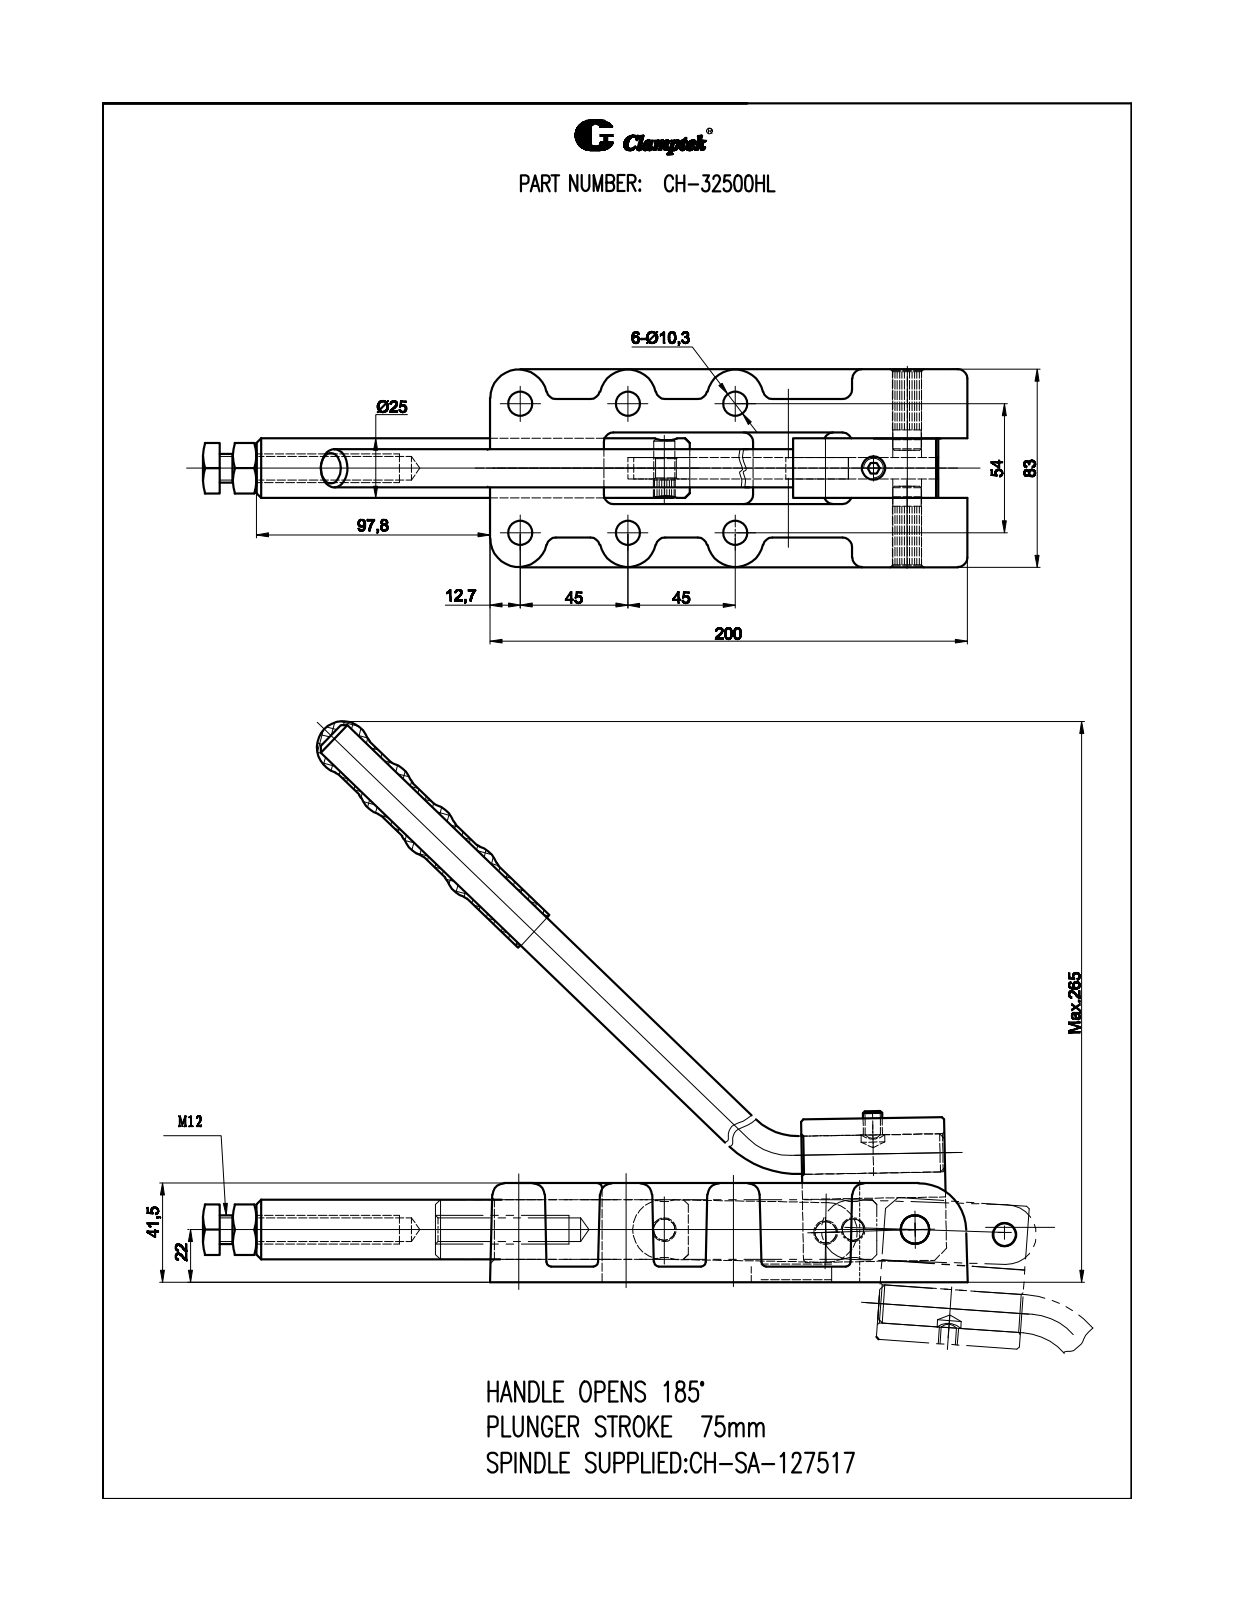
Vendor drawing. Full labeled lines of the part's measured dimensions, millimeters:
Part name (STEP PRODUCT): CH-32500HL
STEP written by: SolidWorks 2008 (CONFIG_CONTROL_DESIGN)
Units: millimetres
Bodies: 13 solids, 1027 faces (273 planar, 336 cylindrical, 418 other)
Overall size (bounding box): 318 × 281.65 × 78
Volume: 586 040 mm³ · Surface area: 159 482 mm²
Round holes (diameter × count): ⌀10.3 ×6, ⌀9.02 ×2, ⌀9.2 ×2, ⌀4 ×1, ⌀6.8 ×1, ⌀9 ×1, ⌀9.05 ×1, ⌀10 ×1, ⌀12 ×1, ⌀12.22 ×1, ⌀15.6 ×1, ⌀16 ×1
Round bosses / shafts (diameter × count): ⌀24.8 ×1, ⌀19.6 ×1, ⌀16 ×1, ⌀12.2 ×1, ⌀11.8 ×1, ⌀9.2 ×1, ⌀9 ×1, ⌀7.95 ×1
Partial cylindrical surfaces — rounded edges, fillets, slot ends (radius × count): R4 ×16, R3 ×9, R2 ×8, R5 ×8, R12 ×6, R1.5 ×2, R12.5 ×2, R20 ×1
Main face-to-face distances: 8.5, 17.31, 2.1, 27.9, 24, 26.1, 51.9, 54, 40, 34.6
Hole centre spacings: 45, 70.29, 54, 90, 104.96, 0.5, 29.76, 37.5
